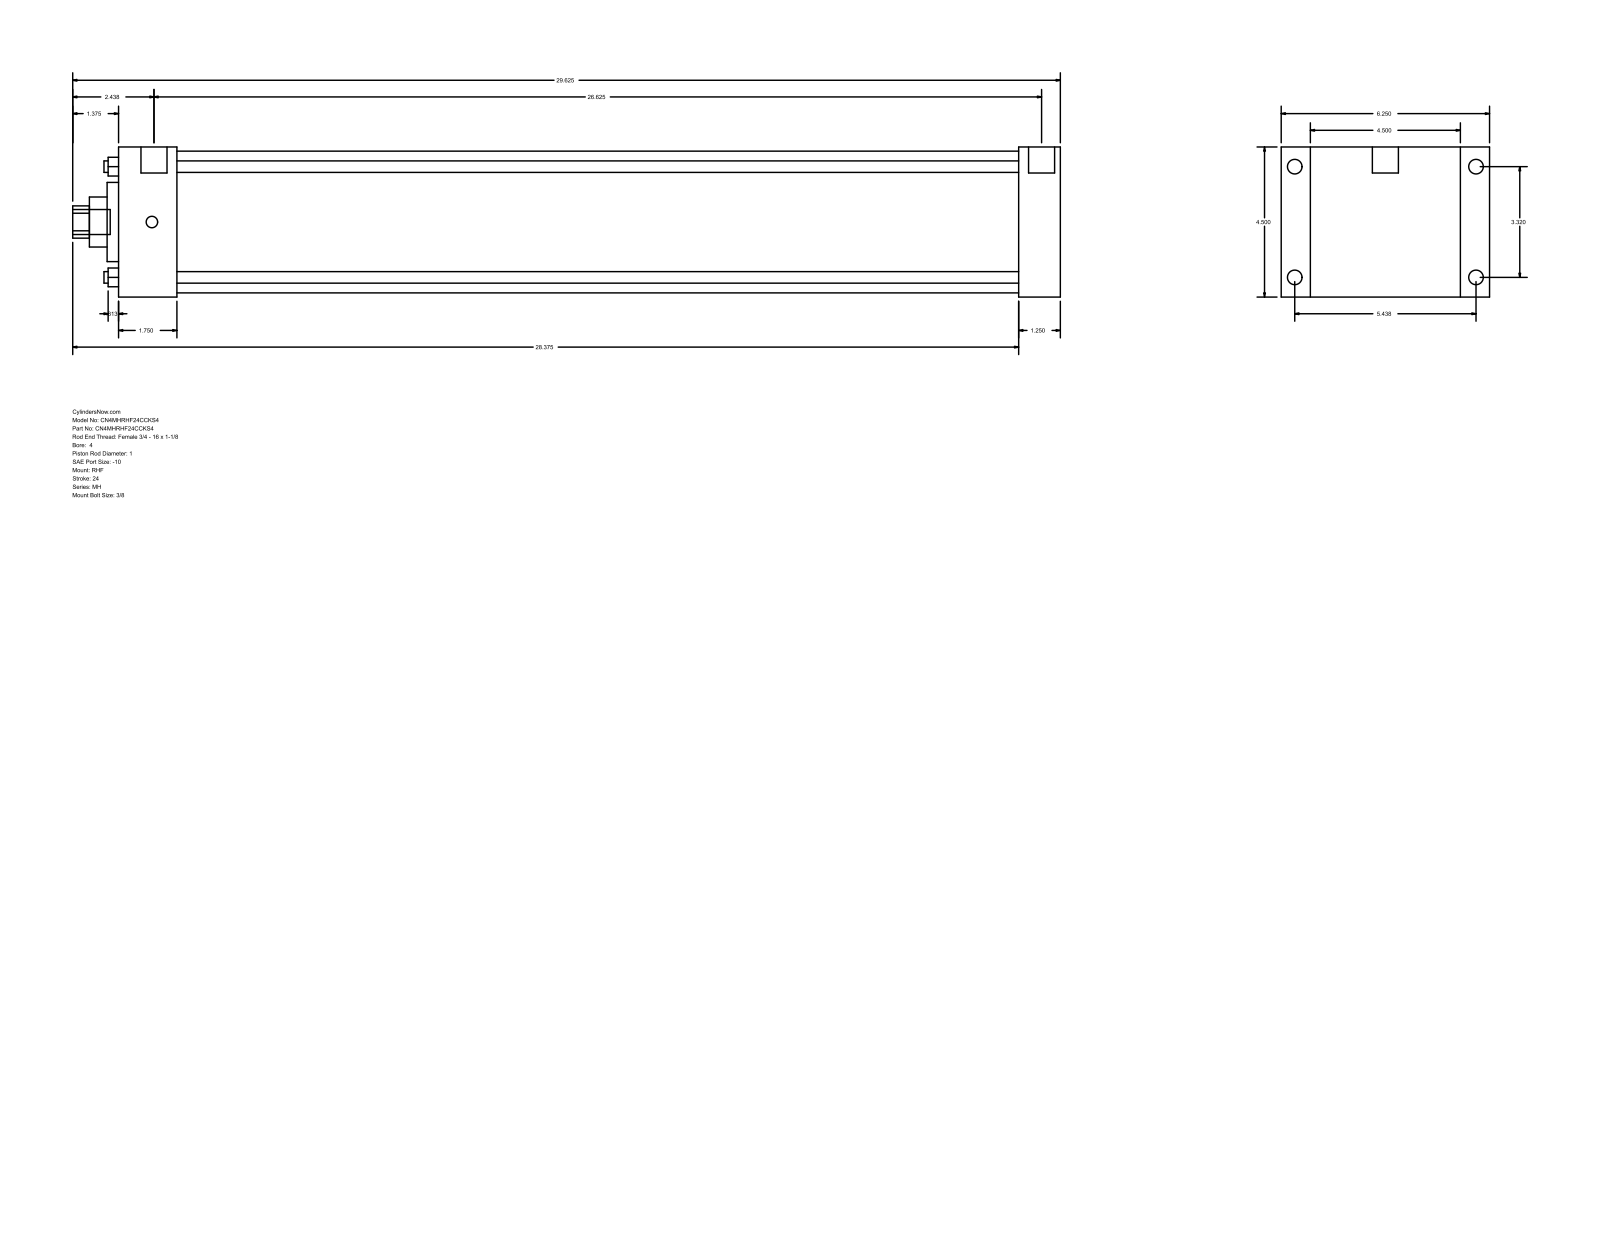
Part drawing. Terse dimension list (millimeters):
name: MH_RHF__0400_1
written by: GSSL Pune (CONFIG_CONTROL_DESIGN)
unit: mm
bodies: 0 solids, 90 faces (61 planar, 29 cylindrical, 0 other)
size: 752.48 × 158.75 × 114.3
holes: 4× ⌀8.76, 1× ⌀25.4, 1× ⌀38.1, 1× ⌀60.33, 1× ⌀107.95
bosses: 4× ⌀11.13, 4× ⌀8.73, 2× ⌀19.84, 1× ⌀19.05
rounds: 1× R12.29
face distances: 114.3, 717.56, 685.81, 31.75, 22.23, 136.53, 44.46, 641.35, 673.1, 158.76
hole spacings: 59.62, 84.32, 119.25
